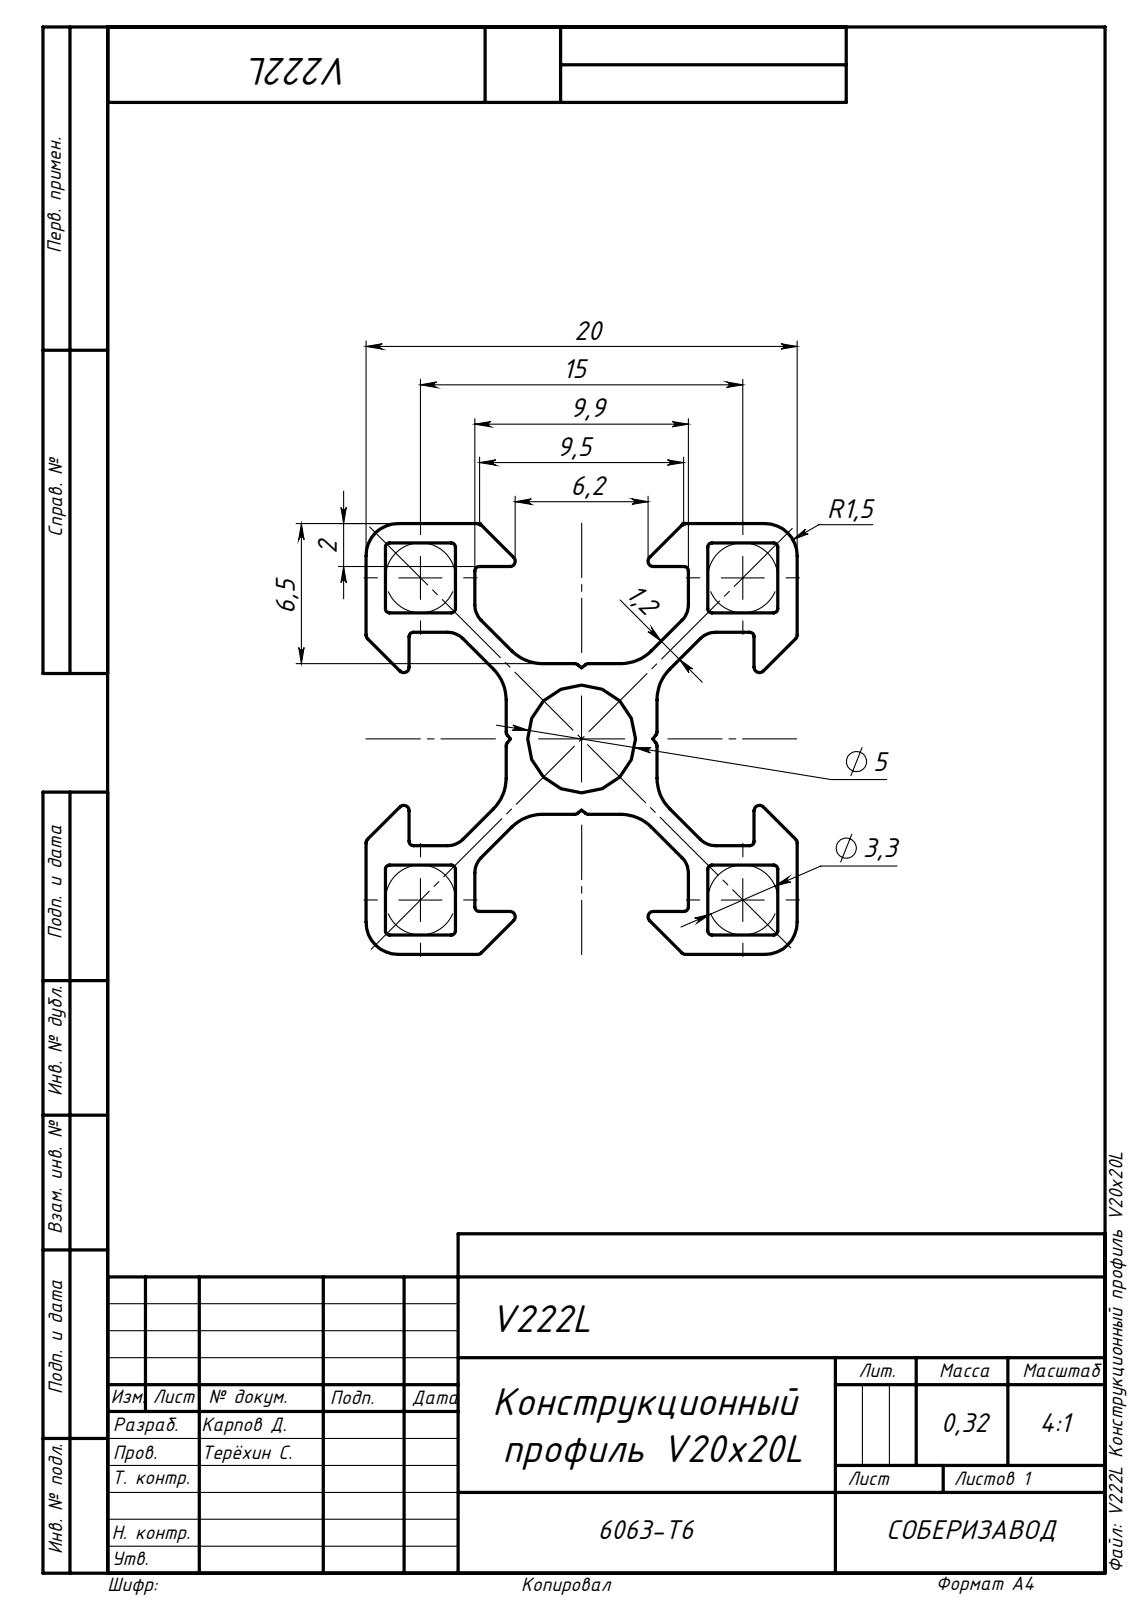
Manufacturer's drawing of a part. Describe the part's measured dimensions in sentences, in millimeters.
Its 3-D file was written by "SolidWorks 2018 (AUTOMOTIVE_DESIGN)". It is 1 solid with 146 faces: 74 planar, 72 cylindrical and 0 other. Overall it measures 1000 by 20 by 20 millimeters. Its volume is 119 724 cubic millimeters and its surface area 205 189 square millimeters. Round holes: 1 of diameter 5. Partial cylindrical surfaces (rounded edges, fillets, slot ends): 24 of radius 0.2, 24 of radius 0.25, 8 of radius 1, 8 of radius 2, 4 of radius 1.5. The main face-to-face distances are 4.15, 0.9, 14.95, 15.85, 19.1, 3.25, 3.13, 4.33, 20, 5.05.
